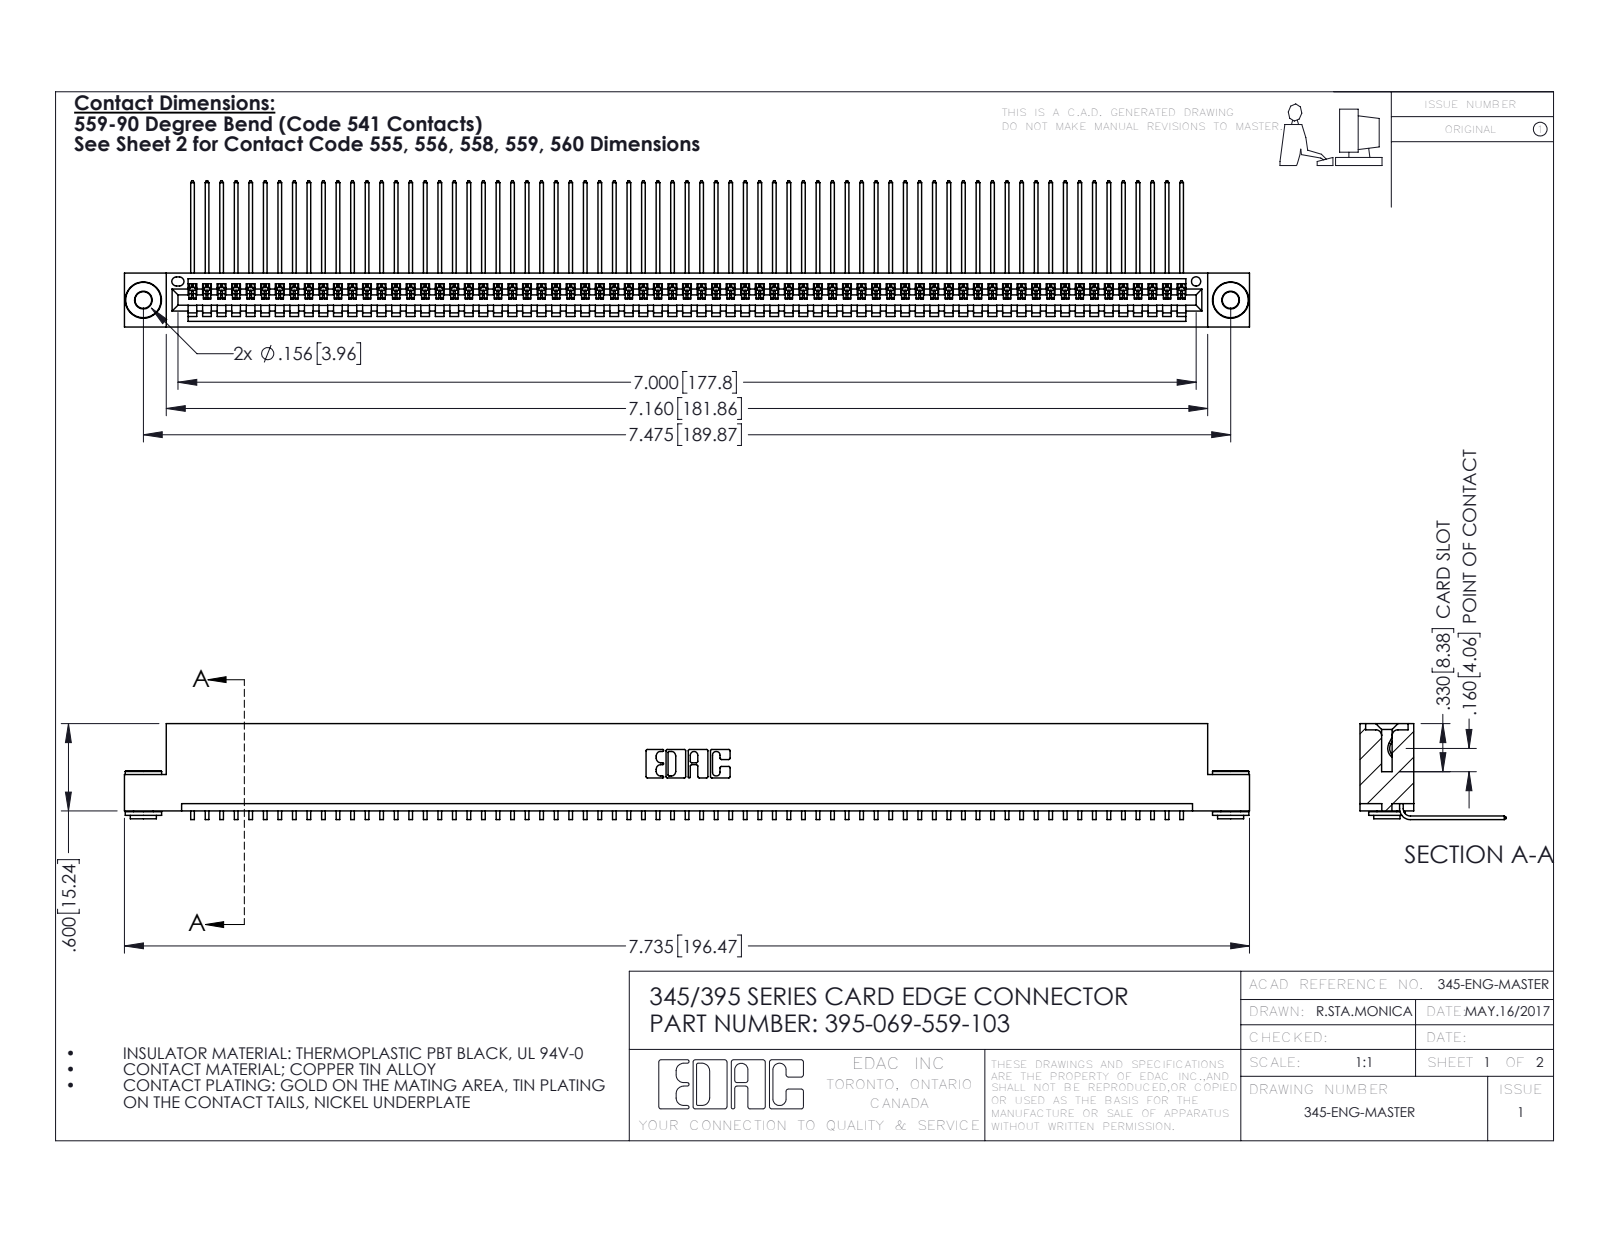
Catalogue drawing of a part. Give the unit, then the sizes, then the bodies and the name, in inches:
Units: inches
Overall size (bounding box): 7.735 × 1.005 × 0.659
Round holes (diameter × count): ⌀0.116 ×2, ⌀0.156 ×2, ⌀0.064 ×1
Round bosses / shafts (diameter × count): ⌀0.25 ×2, ⌀0.18 ×2, ⌀0.136 ×2
Partial cylindrical surfaces — rounded edges, fillets, slot ends (radius × count): R0.006 ×138, R0.01 ×22, R0.007 ×6, R0.031 ×6, R0.026 ×3, R0.031 ×2, R0.04 ×2, R0.014 ×1
Main face-to-face distances: 0.072, 0.298, 0.37, 0.2, 0.025, 0.098, 0.272, 0.225, 0.149, 0.072
Hole centre spacings: 0.27, 7.239, 7.475
Volume: 1.167 in³ · Surface area: 42.4 in²
Bodies: 72 solids, 4304 faces (2988 planar, 1308 cylindrical, 8 other)
Part name (STEP PRODUCT): 345 Part_Flush Mounting Lugs - 0.156 Dia-TH; 345-250-002_345-250-002-102; 395-069-559-103; 345-292-001_558 559 Tail - 1
STEP written by: SolidWorks 2016 (CONFIG_CONTROL_DESIGN)
